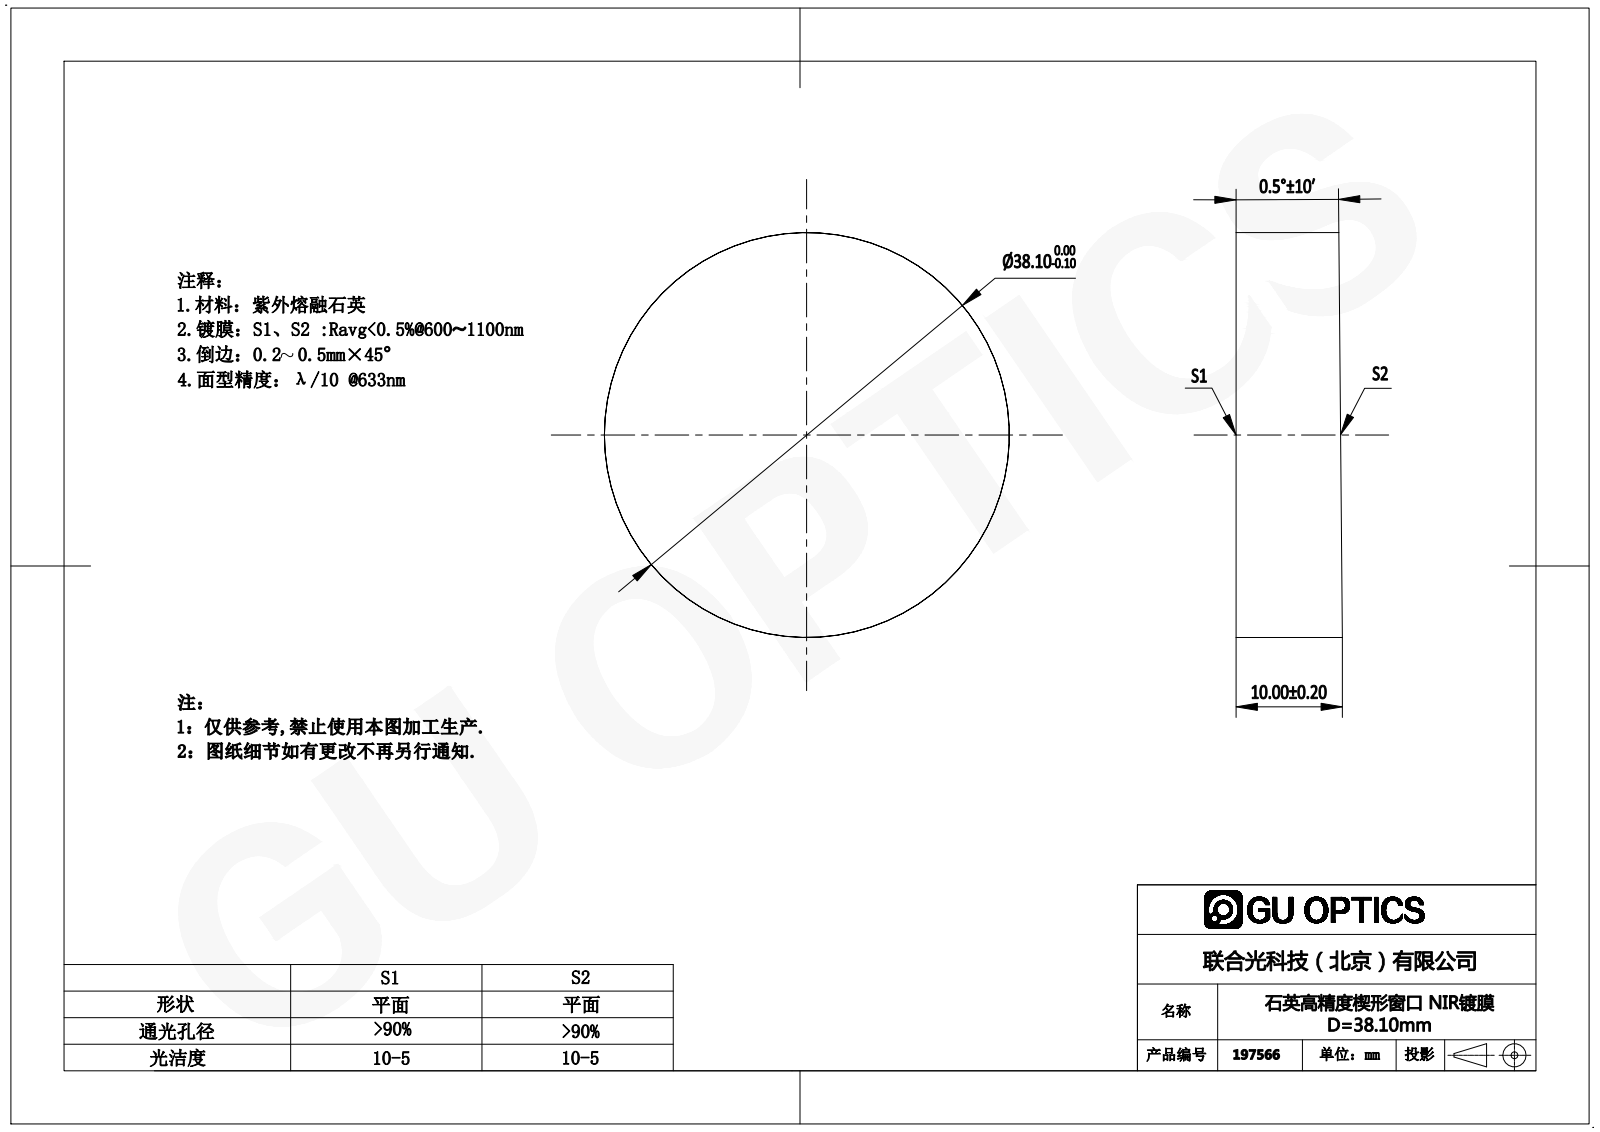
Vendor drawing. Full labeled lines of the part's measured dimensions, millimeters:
Part name (STEP PRODUCT): 197504
STEP written by: SolidWorks 2016 (AUTOMOTIVE_DESIGN)
Units: millimetres
Bodies: 1 solid, 4 faces (2 planar, 2 cylindrical, 0 other)
Overall size (bounding box): 38.1 × 38.1 × 10
Volume: 11 212 mm³ · Surface area: 3 457 mm²
Round bosses / shafts (diameter × count): ⌀38.1 ×1
